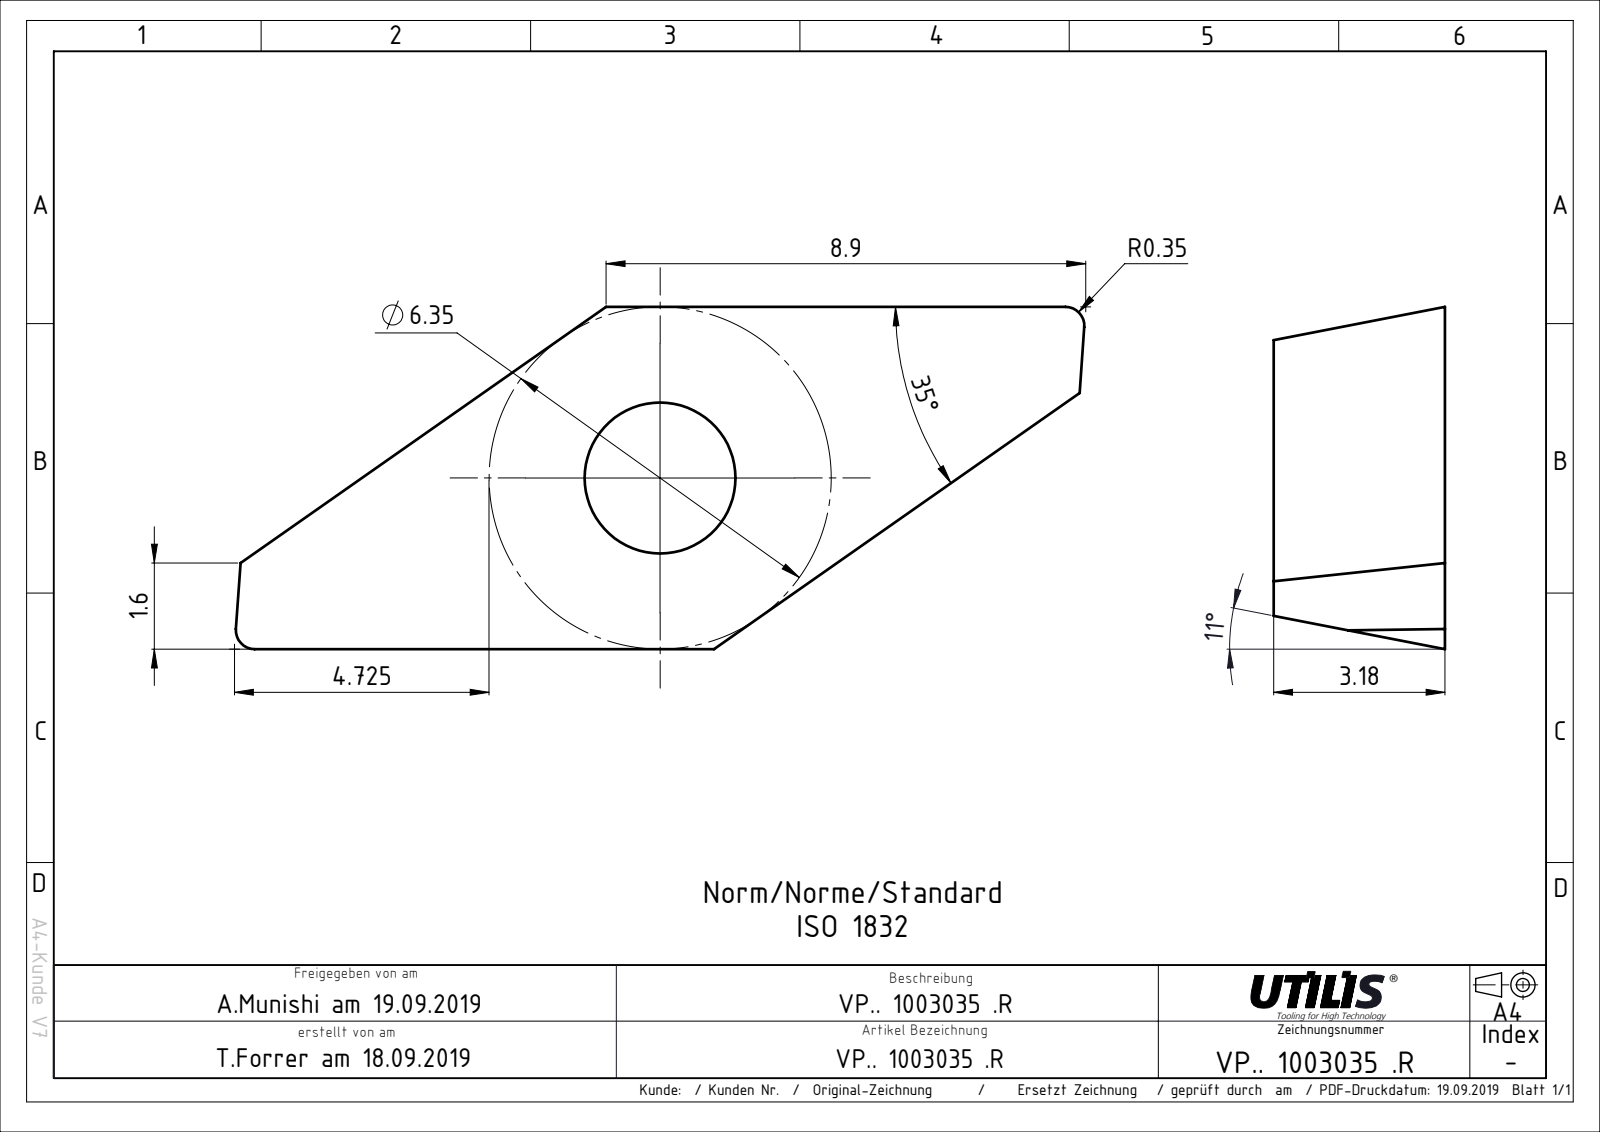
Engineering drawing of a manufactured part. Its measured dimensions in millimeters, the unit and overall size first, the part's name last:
Units: millimetres
Overall size (bounding box): 15.75 × 6.35 × 3.18
Round holes (diameter × count): ⌀2.8 ×1
Main face-to-face distances: 3.18
Volume: 157 mm³ · Surface area: 241 mm²
Bodies: 1 solid, 13 faces (8 planar, 2 cylindrical, 3 other)
Part name (STEP PRODUCT): VP.. 1003035 .R
STEP written by: SolidWorks 2016 (AUTOMOTIVE_DESIGN)
